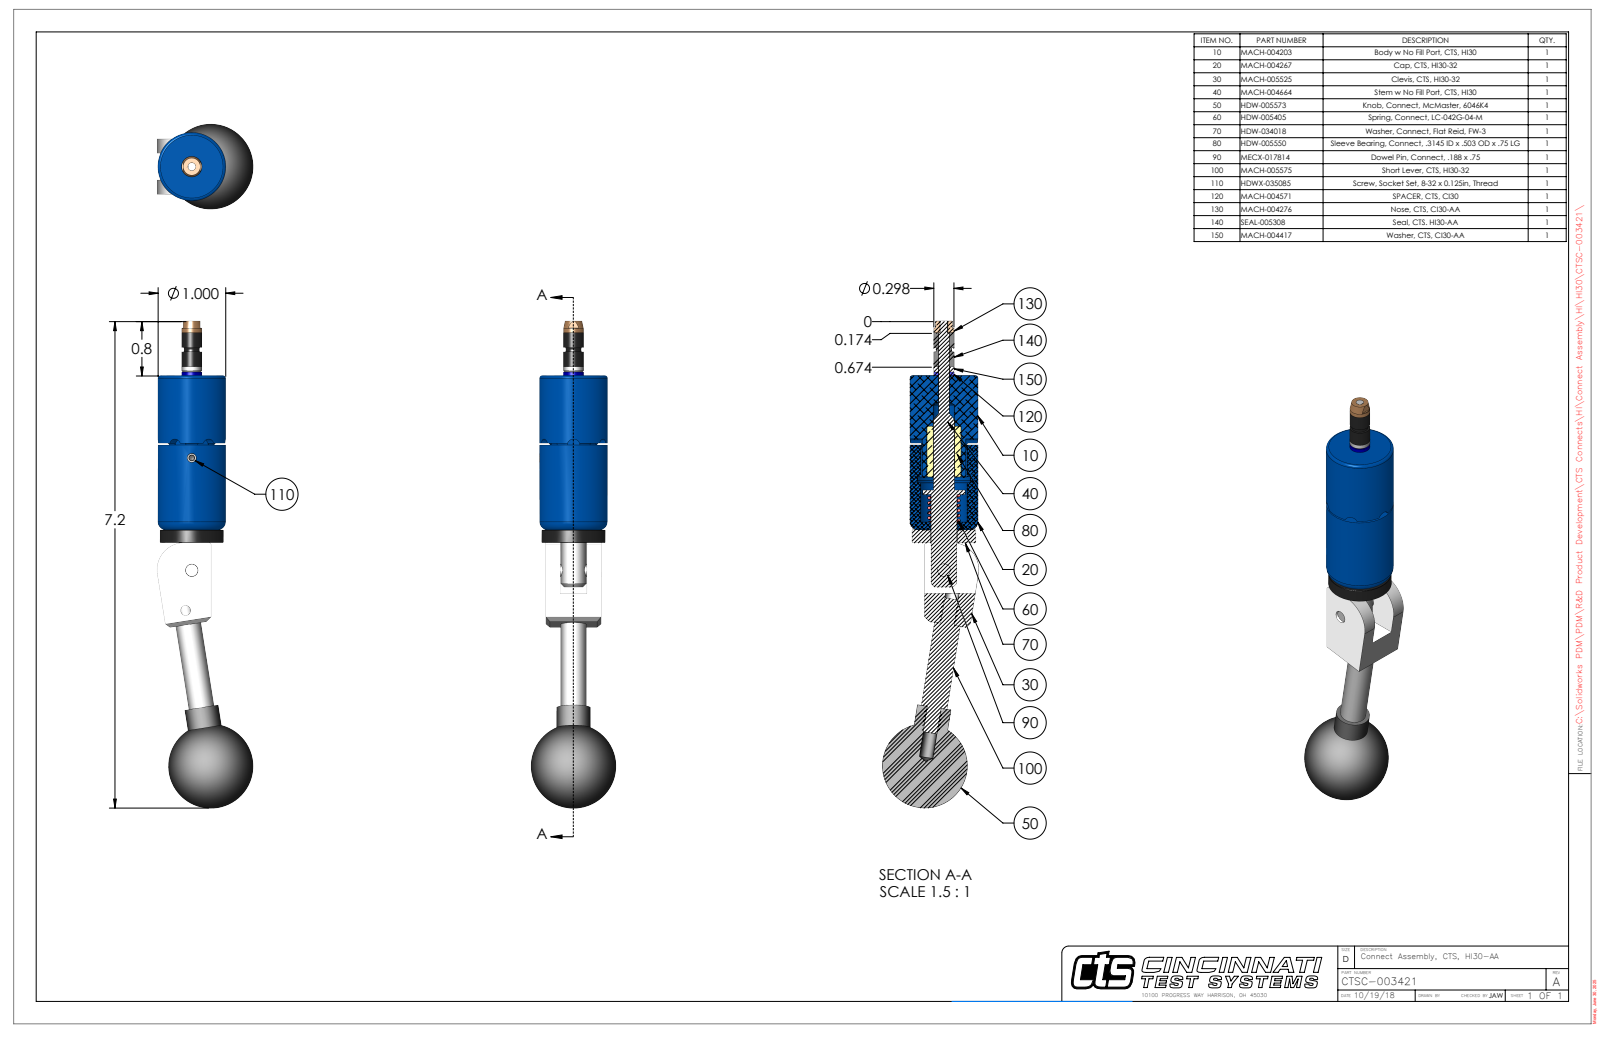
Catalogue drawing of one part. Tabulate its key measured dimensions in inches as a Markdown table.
| quantity | value |
| --- | --- |
| part name | CTSC-003421 |
| STEP written by | SolidWorks 2023 (AUTOMOTIVE_DESIGN) |
| units | inches |
| bodies | 10 solids, 253 faces (96 planar, 100 cylindrical, 57 other) |
| overall size | 7.193 × 1.416 × 1.25 |
| volume | 3.708 in³ |
| surface area | 29.22 in² |
| round holes (diameter × count) | 0.201 × 2, 0.113 × 1, 0.136 × 1, 0.15 × 1, 0.155 × 1, 0.161 × 1, 0.164 × 1, 0.189 × 1, 0.385 × 1, 0.392 × 1 |
| round bosses / shafts (diameter × count) | 1 × 1, 0.936 × 1, 0.5 × 1, 0.38 × 1, 0.375 × 1, 0.3 × 1, 0.297 × 1, 0.25 × 1 |
| partial cylindrical surfaces (radius × count) | 0.093 × 6, 0.015 × 1, 0.344 × 1, 0.4 × 1, 0.468 × 1 |
| main face-to-face distances | 0.21, 0.602, 0.812, 0.187, 2.28, 2.467, 0.391, 1.026, 1.253, 1.441 |
| hole center spacings | 0.599, 1.658, 2.252 |
